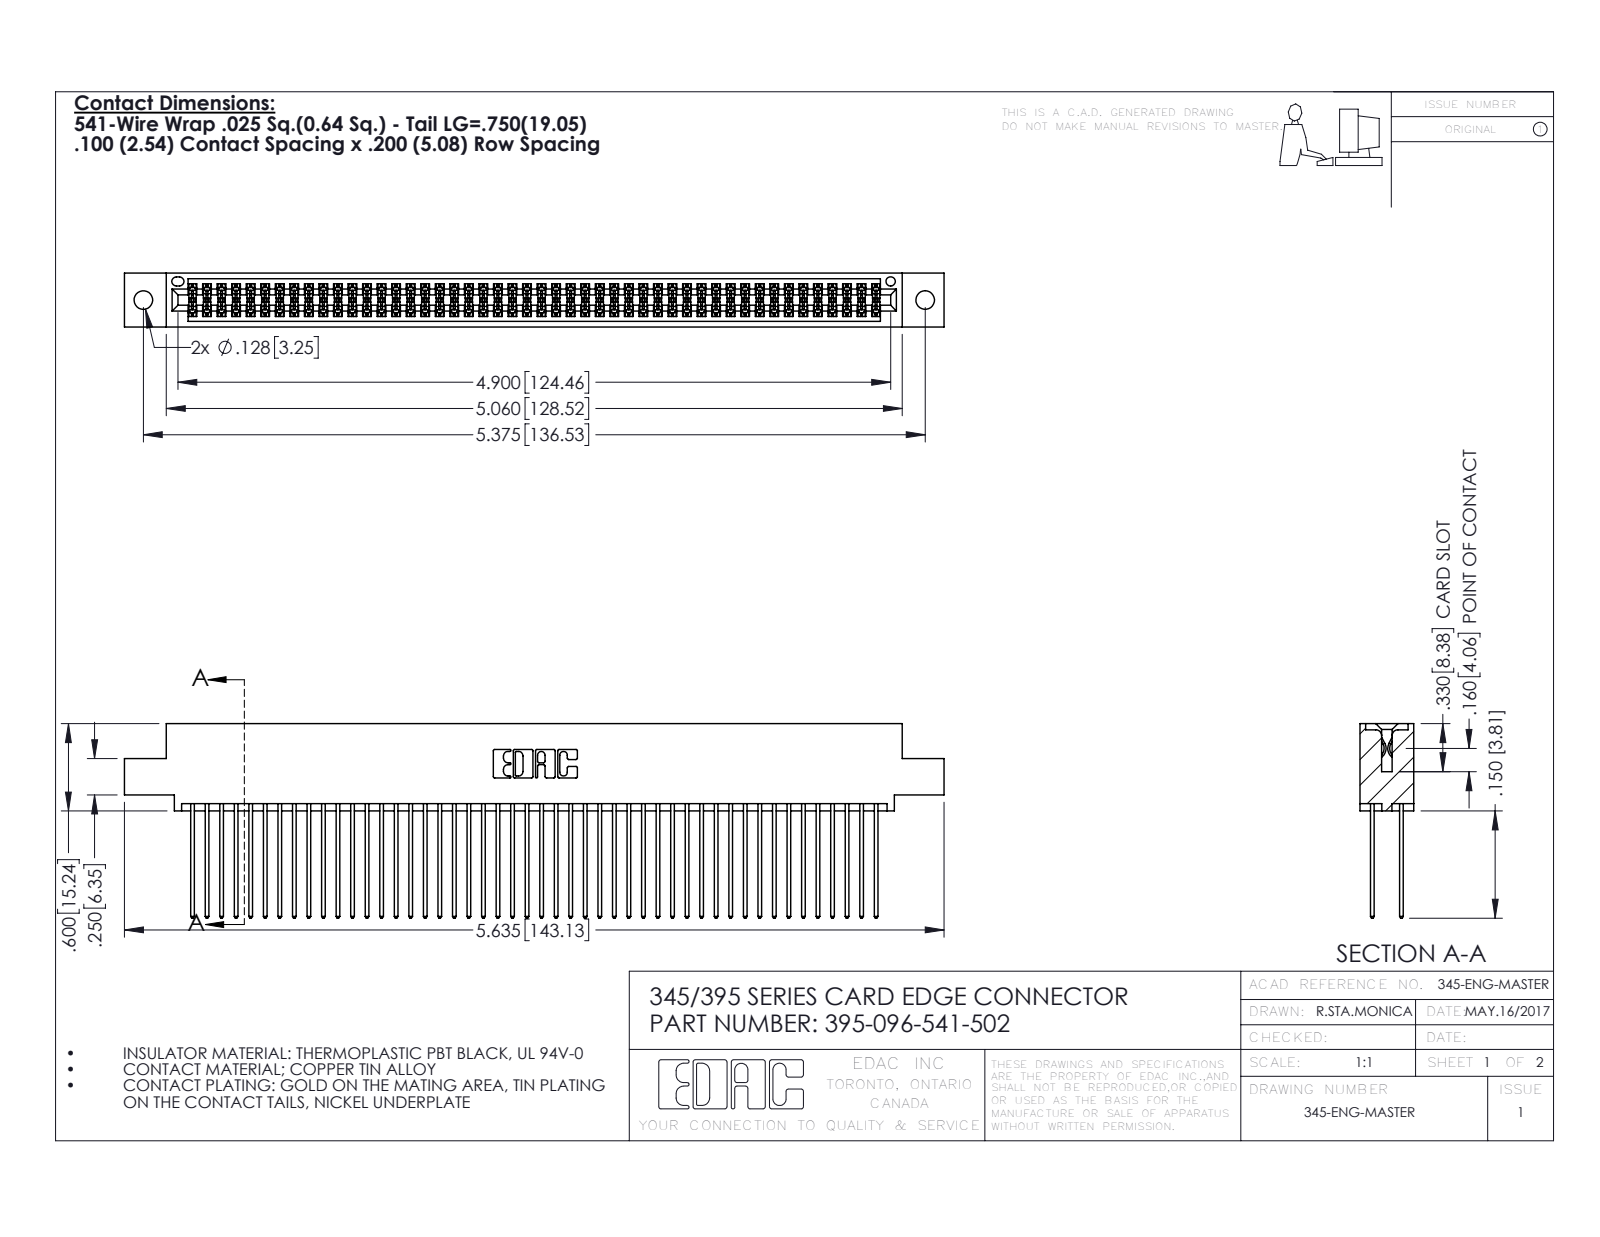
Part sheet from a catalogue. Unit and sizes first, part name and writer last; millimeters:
Units: millimetres
Overall size (bounding box): 143.1 × 34 × 9.4
Round holes (diameter × count): ⌀3.3 ×2, ⌀1.6 ×1
Partial cylindrical surfaces — rounded edges, fillets, slot ends (radius × count): R0.2 ×144, R0.3 ×96, R0.3 ×22, R0.2 ×6, R0.8 ×6, R0.7 ×3, R0.4 ×2, R0.5 ×2
Main face-to-face distances: 7.6, 1.8, 5.1, 2.5, 6.9, 0.6, 5.7, 9.4, 4.4, 3.8
Hole centre spacings: 6.9, 130.5, 136.5
Volume: 14 400 mm³ · Surface area: 23 810 mm²
Bodies: 97 solids, 4930 faces (3252 planar, 1678 cylindrical, 0 other)
Part name (STEP PRODUCT): 345 Part_0.110 Offset - 0.128 Dia; 395-096-541-502; 345-292-001_345-293-141
STEP written by: SolidWorks 2016 (CONFIG_CONTROL_DESIGN)
